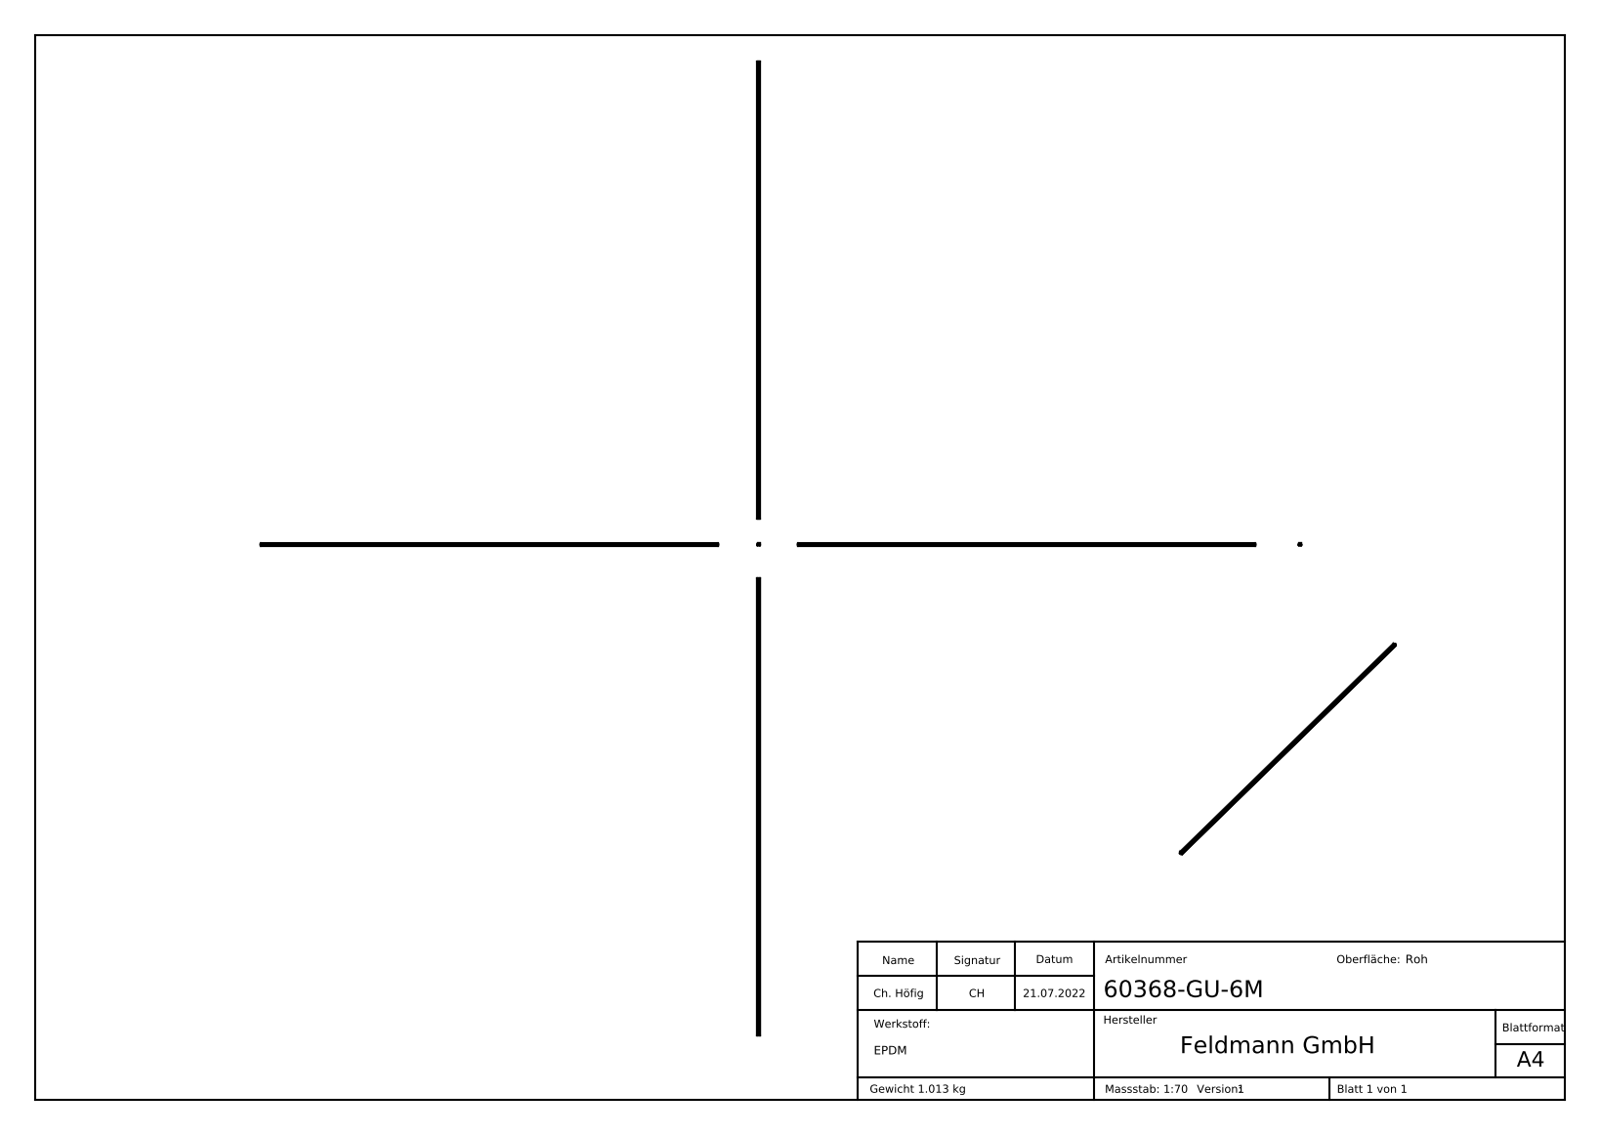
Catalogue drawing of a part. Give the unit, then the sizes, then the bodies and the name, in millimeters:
Units: millimetres
Overall size (bounding box): 6000 × 35 × 32
Partial cylindrical surfaces — rounded edges, fillets, slot ends (radius × count): R0.5 ×4, R1 ×2, R3 ×2, R11 ×2
Main face-to-face distances: 0.8, 26.2, 25.4, 2.5, 27, 1.48, 3.5, 7, 2.97, 4.45
Volume: 857 565 mm³ · Surface area: 1 224 000 mm²
Bodies: 1 solid, 355 faces (194 planar, 10 cylindrical, 151 other)
Part name (STEP PRODUCT): 60368-GU-6M
STEP written by: SolidWorks 2018 (CONFIG_CONTROL_DESIGN)
